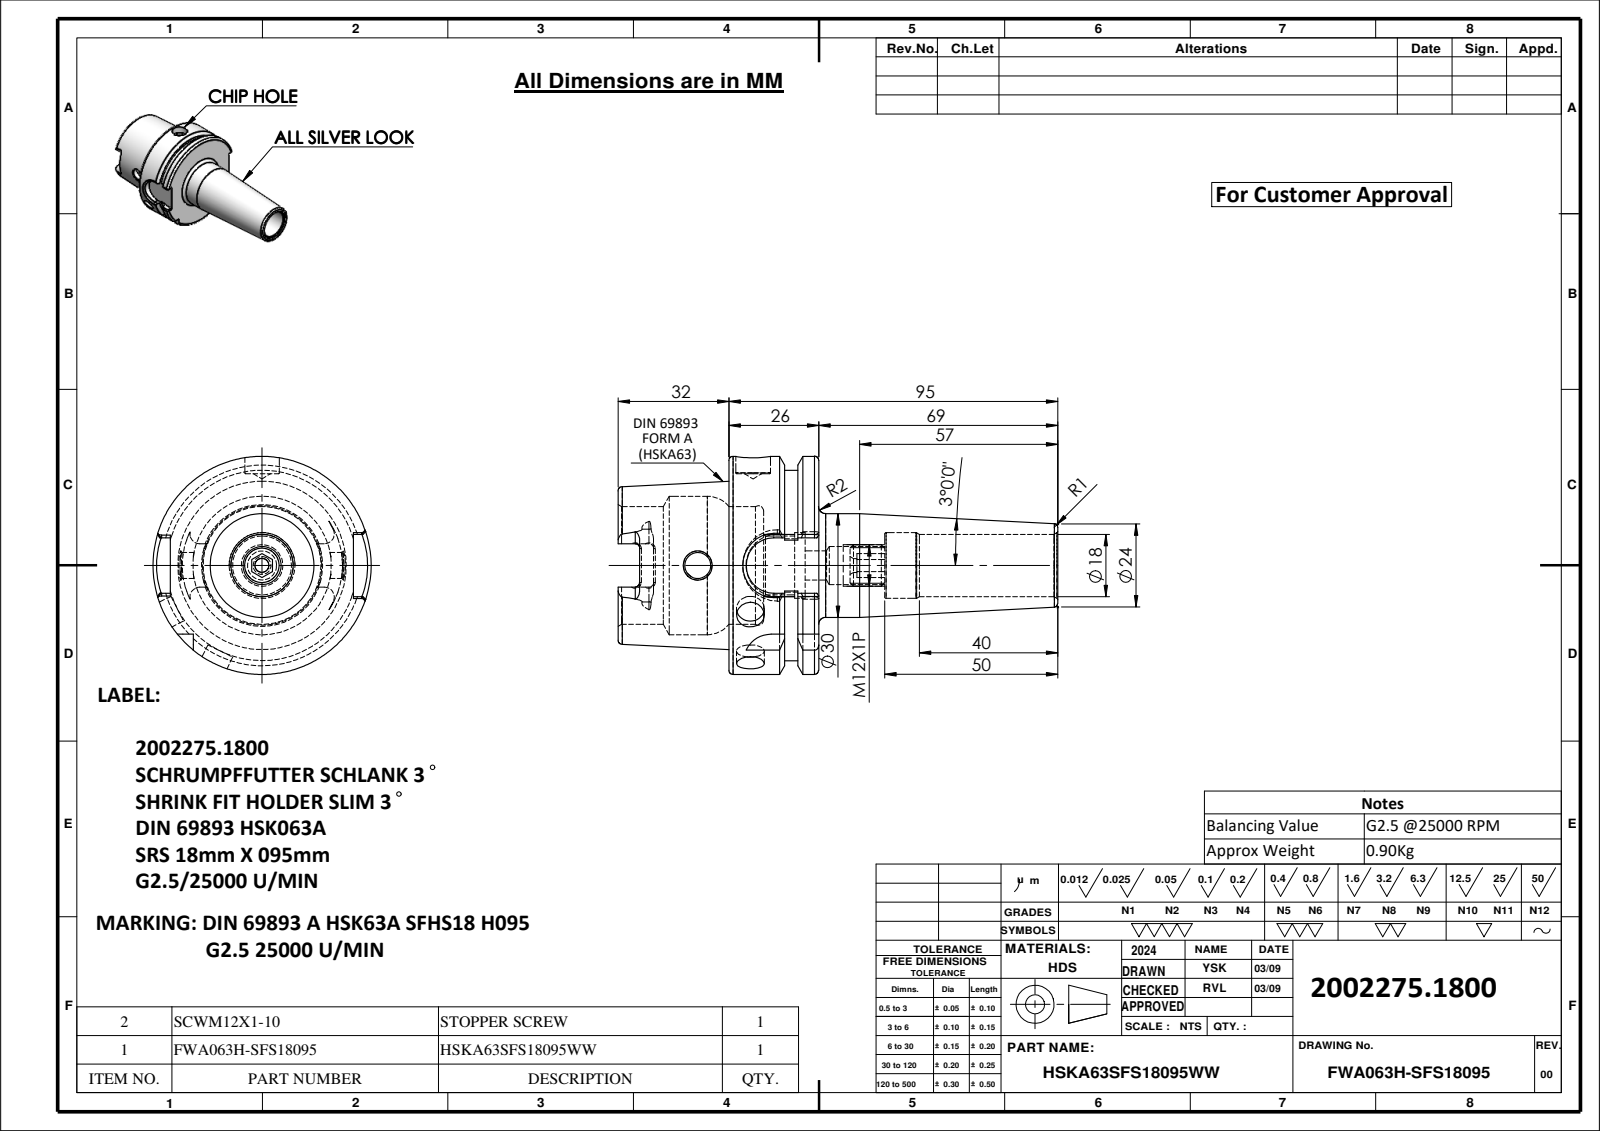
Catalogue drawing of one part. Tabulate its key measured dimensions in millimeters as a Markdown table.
| quantity | value |
| --- | --- |
| part name | HSKA63SFS18095WW; SCWM12X1-10; FWA063H-SFS18095 |
| STEP written by | SolidWorks 2024 (CONFIG_CONTROL_DESIGN) |
| units | millimeters |
| bodies | 2 solids, 196 faces (59 planar, 57 cylindrical, 80 other) |
| overall size | 127 × 63 × 63 |
| volume | 108 228 mm³ |
| surface area | 32 144 mm² |
| round holes (diameter × count) | 8 × 2, 4 × 1, 7.5 × 1, 8.4 × 1, 10 × 1, 11 × 1, 17 × 1, 18 × 1, 19 × 1, 34 × 1, 40 × 1 |
| round bosses / shafts (diameter × count) | 63 × 1, 55 × 1, 30 × 1, 12 × 1 |
| partial cylindrical surfaces (radius × count) | 1.3 × 6, 2.88 × 4, 8 × 2, 9 × 1 |
| main face-to-face distances | 25.95, 10, 15.95, 32, 42, 57.95, 52.9, 35, 54, 22 |
